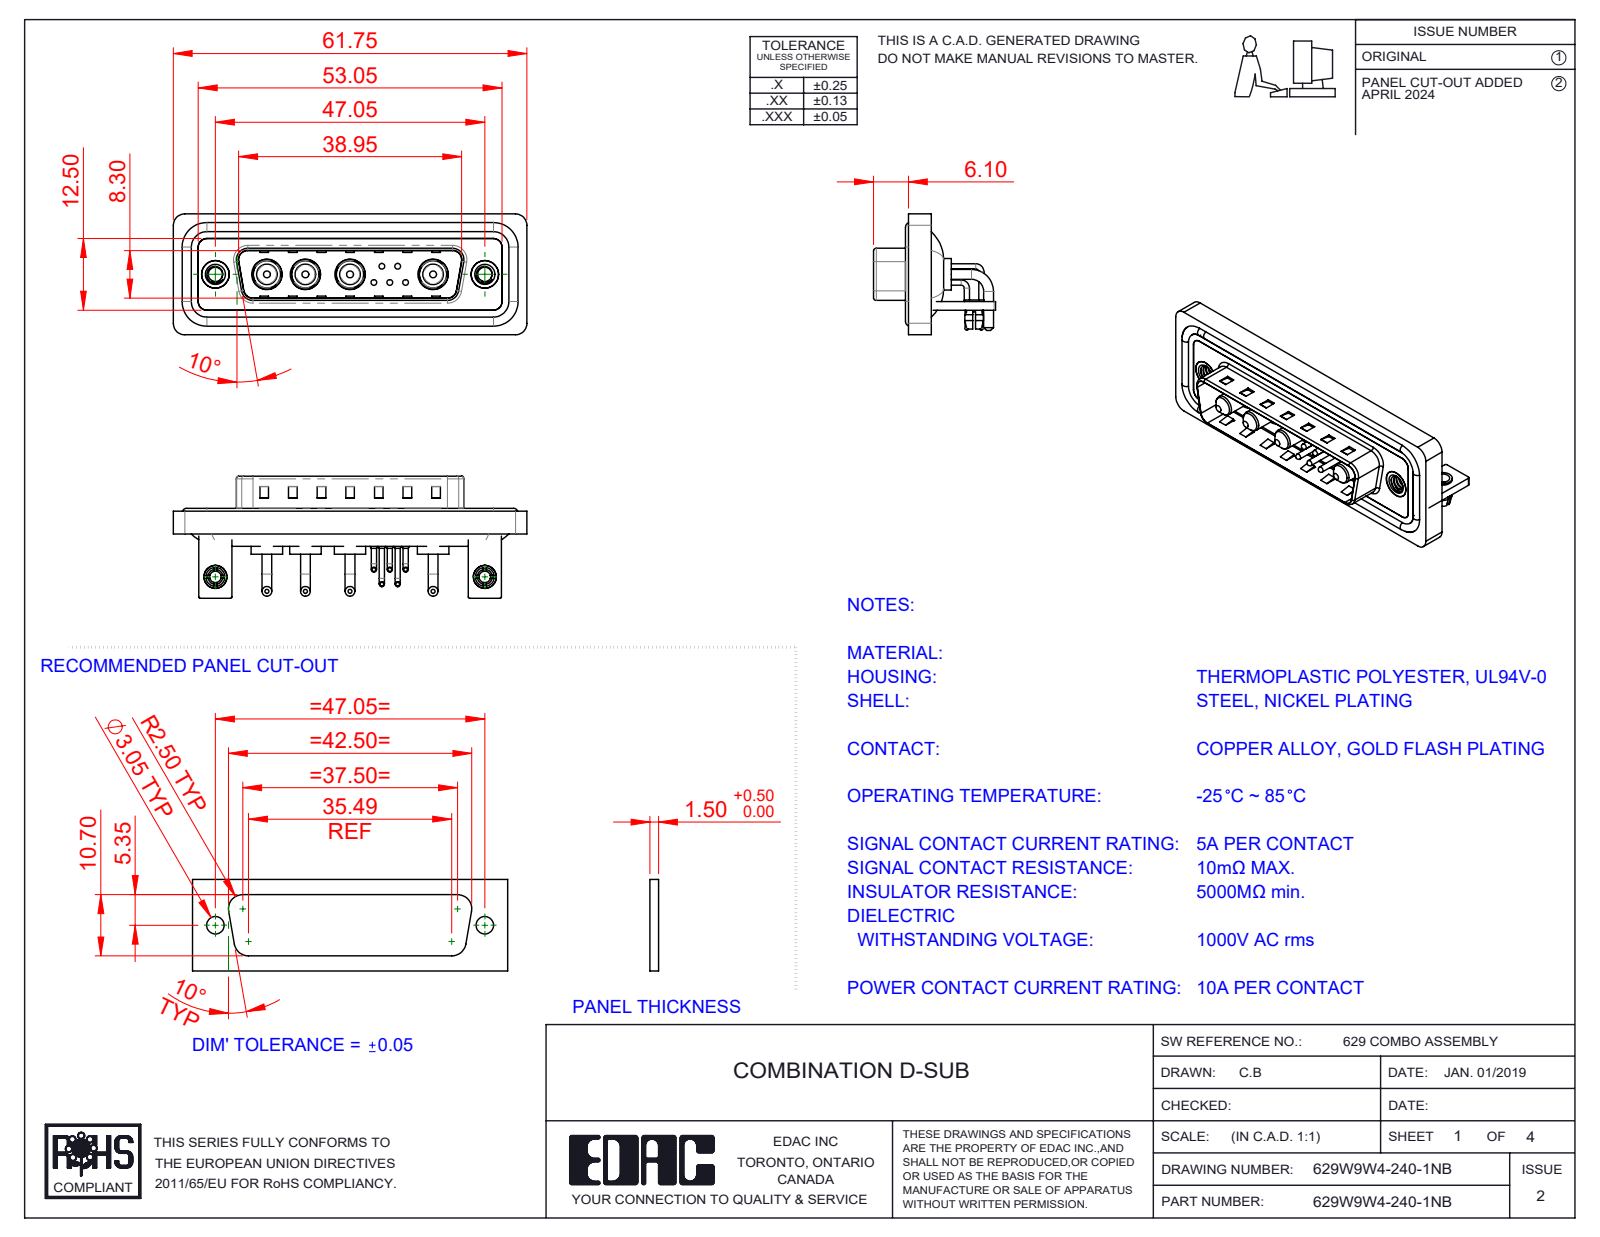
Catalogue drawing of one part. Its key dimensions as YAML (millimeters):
part_name: "629Combo Waterproof Housing_25 Contacts; 629W9W4-240-1NB; 629Combo Threaded Rivet_B; 629Combo Board Lock (+7 more)"
step_written_by: "SolidWorks 2023 (CONFIG_CONTROL_DESIGN)"
units: millimeters
bodies: {solids: 24, faces: 1335, planar: 637, cylindrical: 502, other: 196}
overall_size: [61.75, 21.3, 21.1]
volume: 7780
surface_area: 12971
round_holes:
  - {diameter: 2, count: 7}
  - {diameter: 0.75, count: 5}
  - {diameter: 1.6, count: 5}
  - {diameter: 2.5, count: 4}
  - {diameter: 4.85, count: 4}
  - {diameter: 5.3, count: 4}
  - {diameter: 3.2, count: 2}
  - {diameter: 4, count: 2}
  - {diameter: 4.8, count: 2}
  - {diameter: 5, count: 2}
round_bosses_or_shafts:
  - {diameter: 0.9, count: 10}
  - {diameter: 1.7, count: 8}
  - {diameter: 1.5, count: 5}
  - {diameter: 1, count: 5}
  - {diameter: 0.65, count: 5}
  - {diameter: 5.5, count: 4}
  - {diameter: 5.2, count: 4}
  - {diameter: 4.75, count: 4}
partial_cylinders:
  - {radius: 2, count: 19}
  - {radius: 1.5, count: 18}
  - {radius: 0.25, count: 16}
  - {radius: 0.5, count: 9}
  - {radius: 1.6, count: 8}
  - {radius: 1.01, count: 5}
  - {radius: 0.6, count: 4}
  - {radius: 0.65, count: 4}
face_to_face_distances: [0.4, 1.5, 0.8, 2.9, 2.1, 1.1, 3.7, 4.1, 4.5, 1.6]
hole_center_spacings: [3.16, 2.77, 5.04, 14.5, 47.05, 2.78, 4.4, 4.41]
